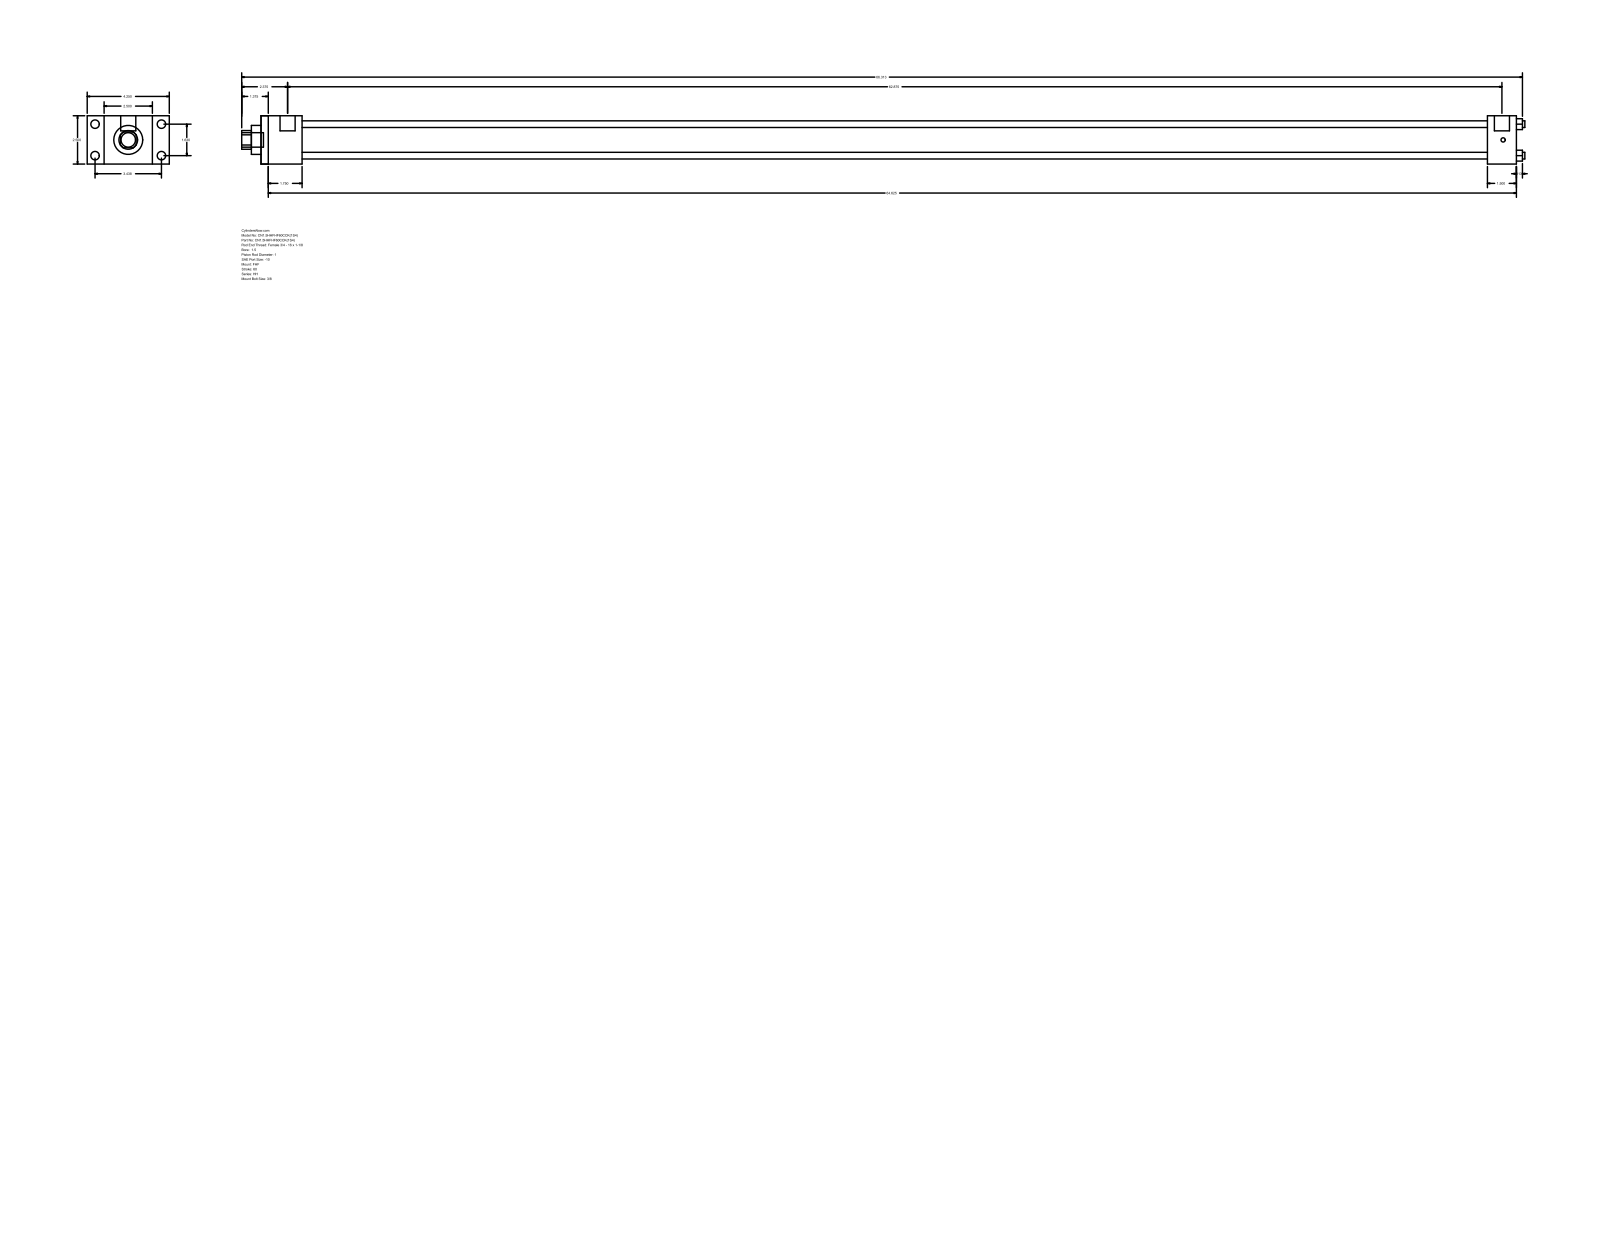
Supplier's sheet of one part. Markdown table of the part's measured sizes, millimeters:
| quantity | value |
| --- | --- |
| part name | HH_FHF__0150_1 |
| STEP written by | GSSL Pune (CONFIG_CONTROL_DESIGN) |
| units | millimeters |
| bodies | 0 solids, 88 faces (60 planar, 28 cylindrical, 0 other) |
| overall size | 1687.51 × 107.95 × 63.5 |
| round holes (diameter × count) | 8.76 × 4, 25.4 × 1, 38.1 × 1, 44.45 × 1 |
| round bosses / shafts (diameter × count) | 11.13 × 4, 5.56 × 4, 19.84 × 2, 19.05 × 1 |
| partial cylindrical surfaces (radius × count) | 12.29 × 1 |
| main face-to-face distances | 63.5, 22.23, 85.73, 53.98, 107.96, 1651, 1597.02, 1612.9, 1558.92, 38.1 |
| hole center spacings | 29.27, 41.4, 58.55 |
